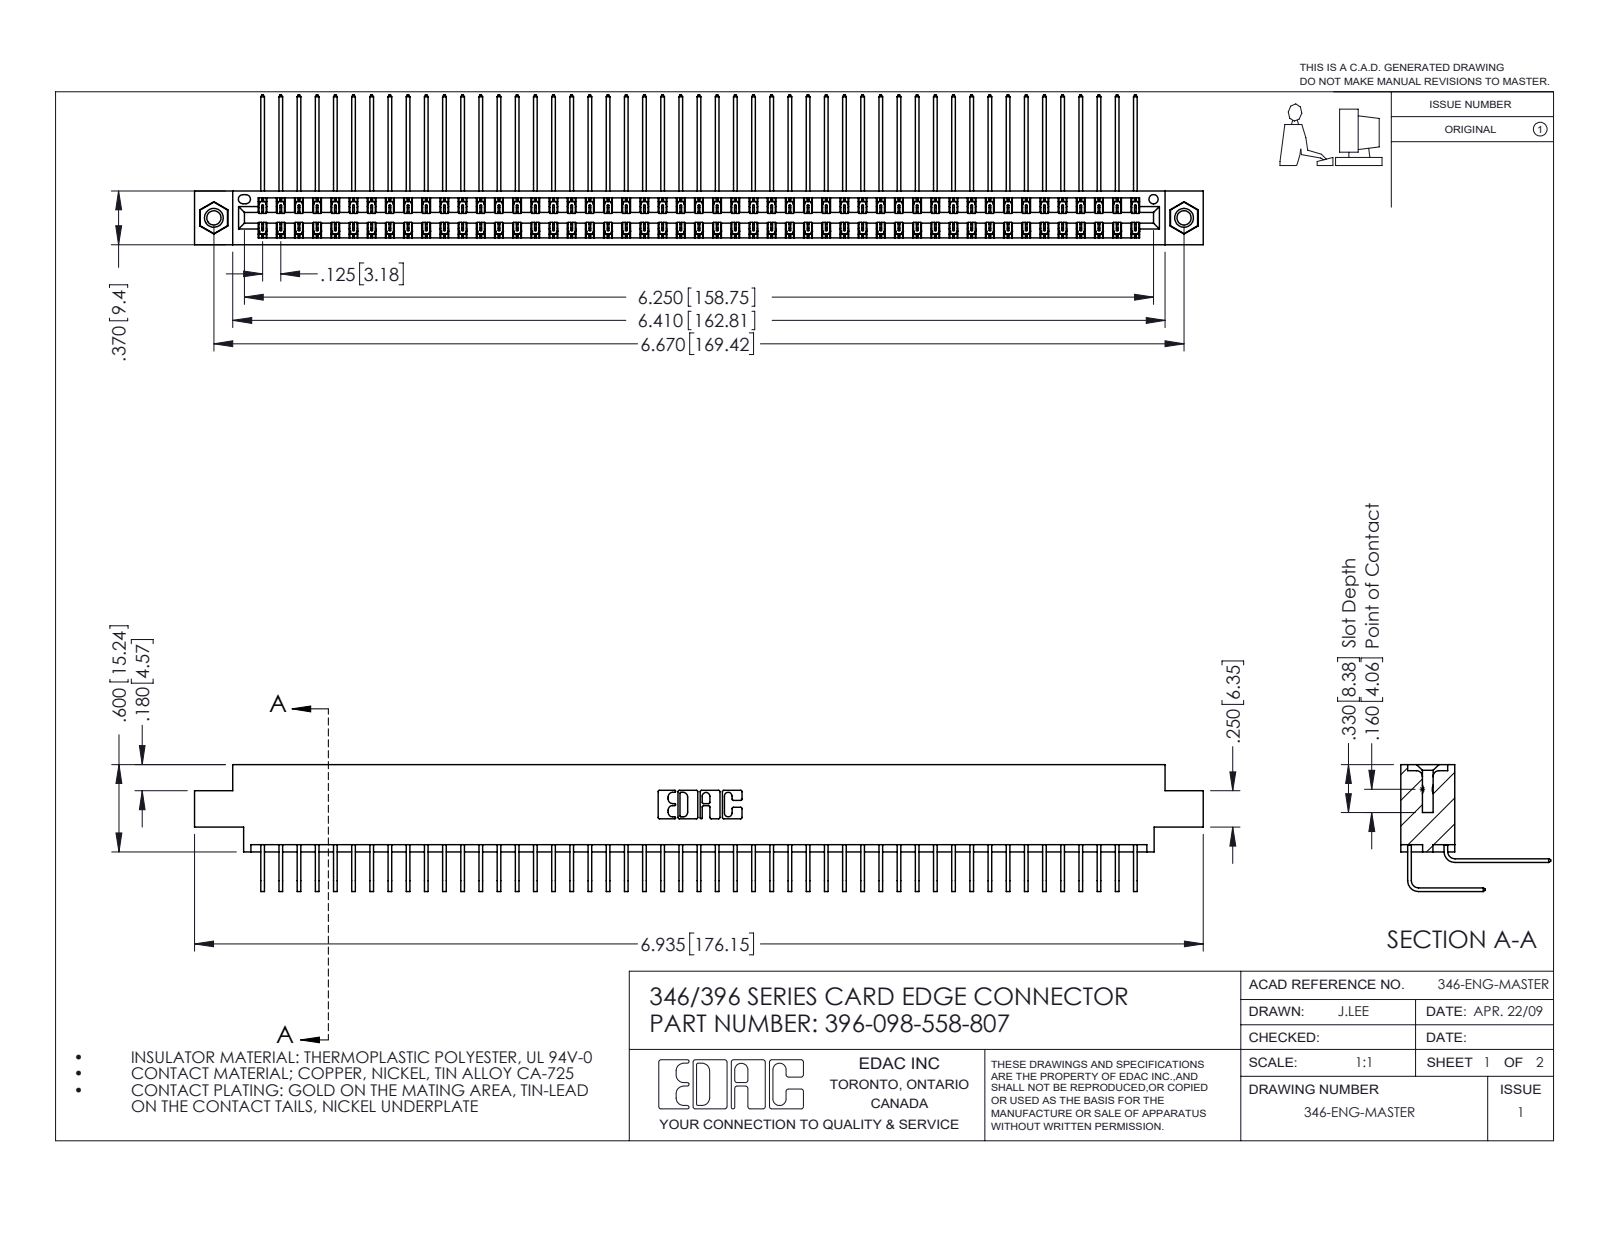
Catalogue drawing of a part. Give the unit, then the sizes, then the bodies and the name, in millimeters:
Units: millimetres
Overall size (bounding box): 176.1 × 26.2 × 22.2
Round holes (diameter × count): ⌀2.5 ×2, ⌀3.2 ×2, ⌀4 ×2, ⌀1.6 ×1
Round bosses / shafts (diameter × count): ⌀3.9 ×2
Partial cylindrical surfaces — rounded edges, fillets, slot ends (radius × count): R0.2 ×147, R0.3 ×22, R0.2 ×6, R0.8 ×6, R0.7 ×3, R0.4 ×2, R0.6 ×2, R0.6 ×2
Main face-to-face distances: 8.2, 1.2, 0.6, 9.4, 6.4, 7.6, 1.8, 7, 5.6, 3.8
Hole centre spacings: 6.2, 164.1, 169.4
Volume: 17 630 mm³ · Surface area: 27 260 mm²
Bodies: 101 solids, 5478 faces (3738 planar, 1724 cylindrical, 16 other)
Part name (STEP PRODUCT): 396-098-558-807; 345-292-001_558 Tail - 2; 345-292-001_558 559 Tail - 1; 345-250-001_345-250-005-103 (+1 more)
STEP written by: SolidWorks 2016 (CONFIG_CONTROL_DESIGN)
